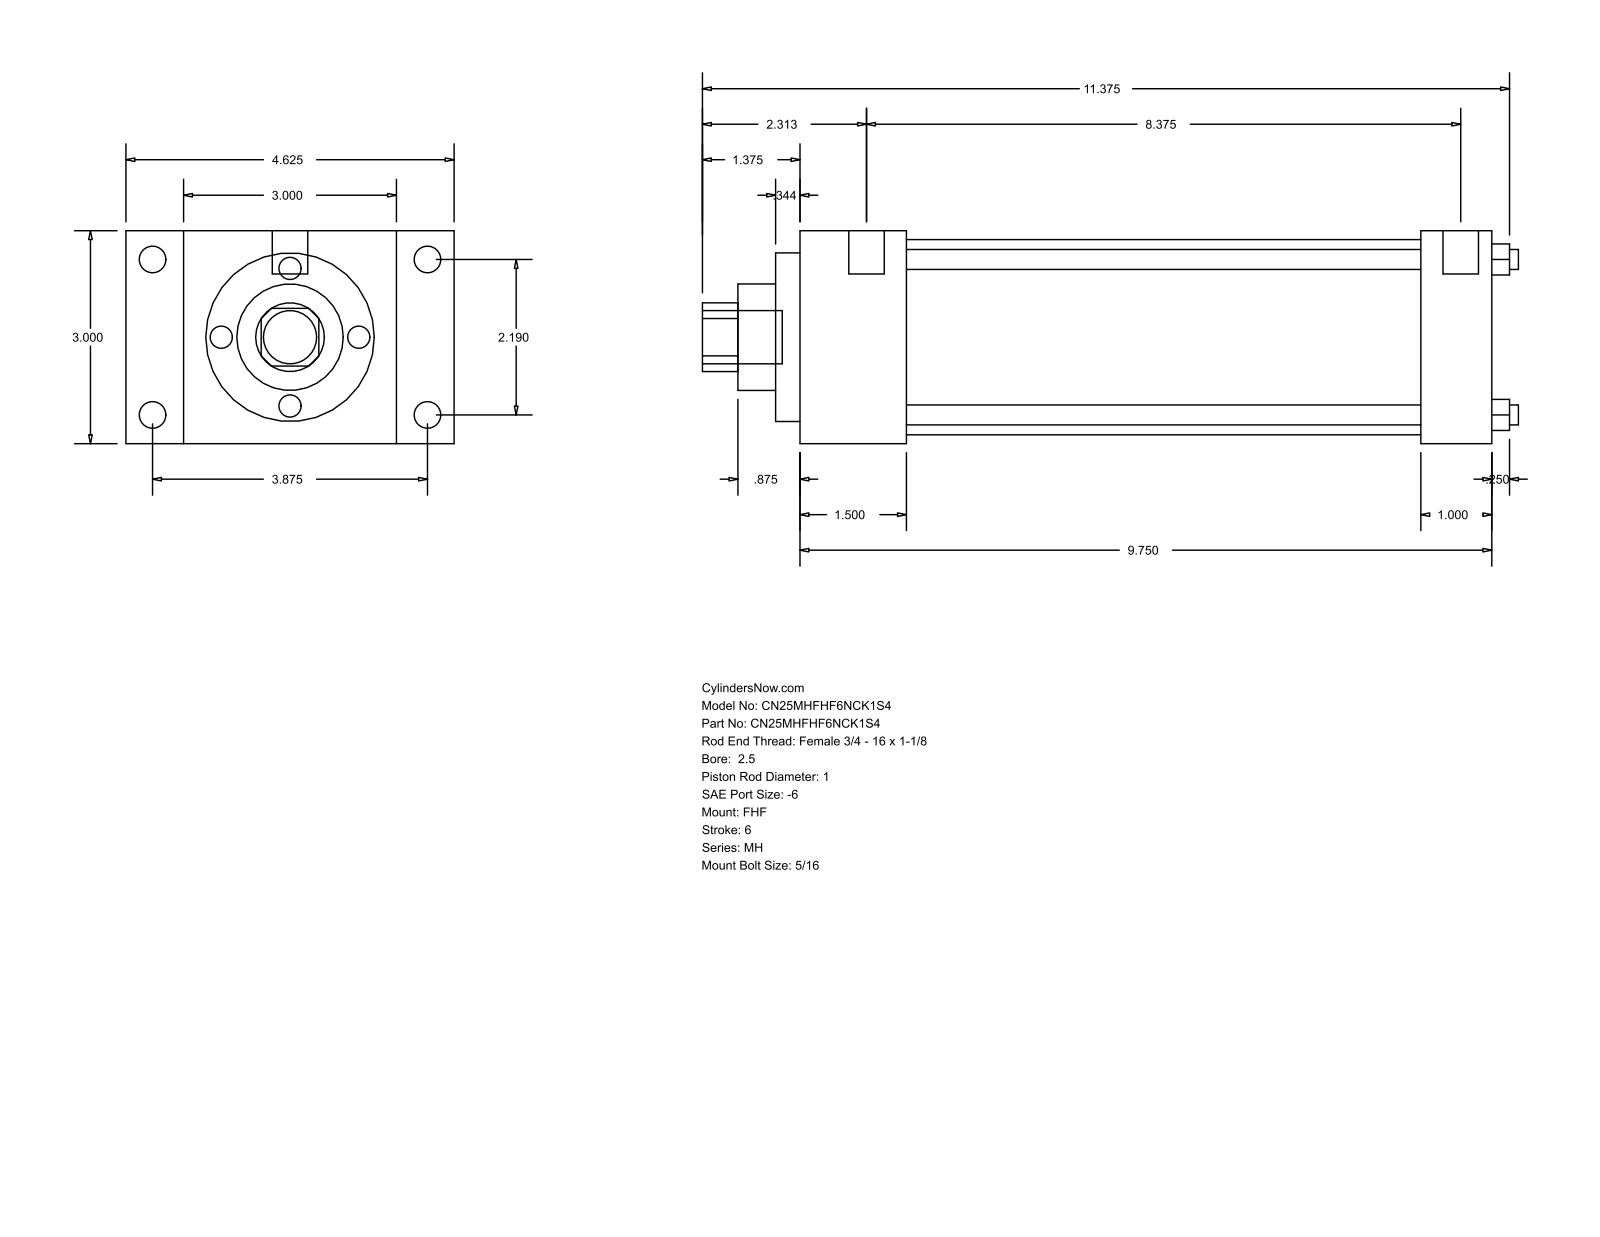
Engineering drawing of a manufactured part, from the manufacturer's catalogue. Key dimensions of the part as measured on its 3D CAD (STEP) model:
Part name (STEP PRODUCT): MH_FHF__0250_1
STEP written by: GSSL Pune (CONFIG_CONTROL_DESIGN)
Units: millimetres
Bodies: 0 solids, 90 faces (61 planar, 29 cylindrical, 0 other)
Overall size (bounding box): 292.1 × 117.47 × 76.2
Round holes (diameter × count): ⌀7.14 ×4, ⌀25.4 ×1, ⌀38.1 ×1, ⌀60.33 ×1, ⌀69.85 ×1
Round bosses / shafts (diameter × count): ⌀9.53 ×4, ⌀5.56 ×4, ⌀12.7 ×2, ⌀19.05 ×1
Partial cylindrical surfaces — rounded edges, fillets, slot ends (radius × count): R12.29 ×1
Main face-to-face distances: 76.2, 247.65, 38.11, 209.54, 20.64, 96.84, 117.48, 25.39, 222.26, 184.15
Hole centre spacings: 39.33, 55.62, 78.66
